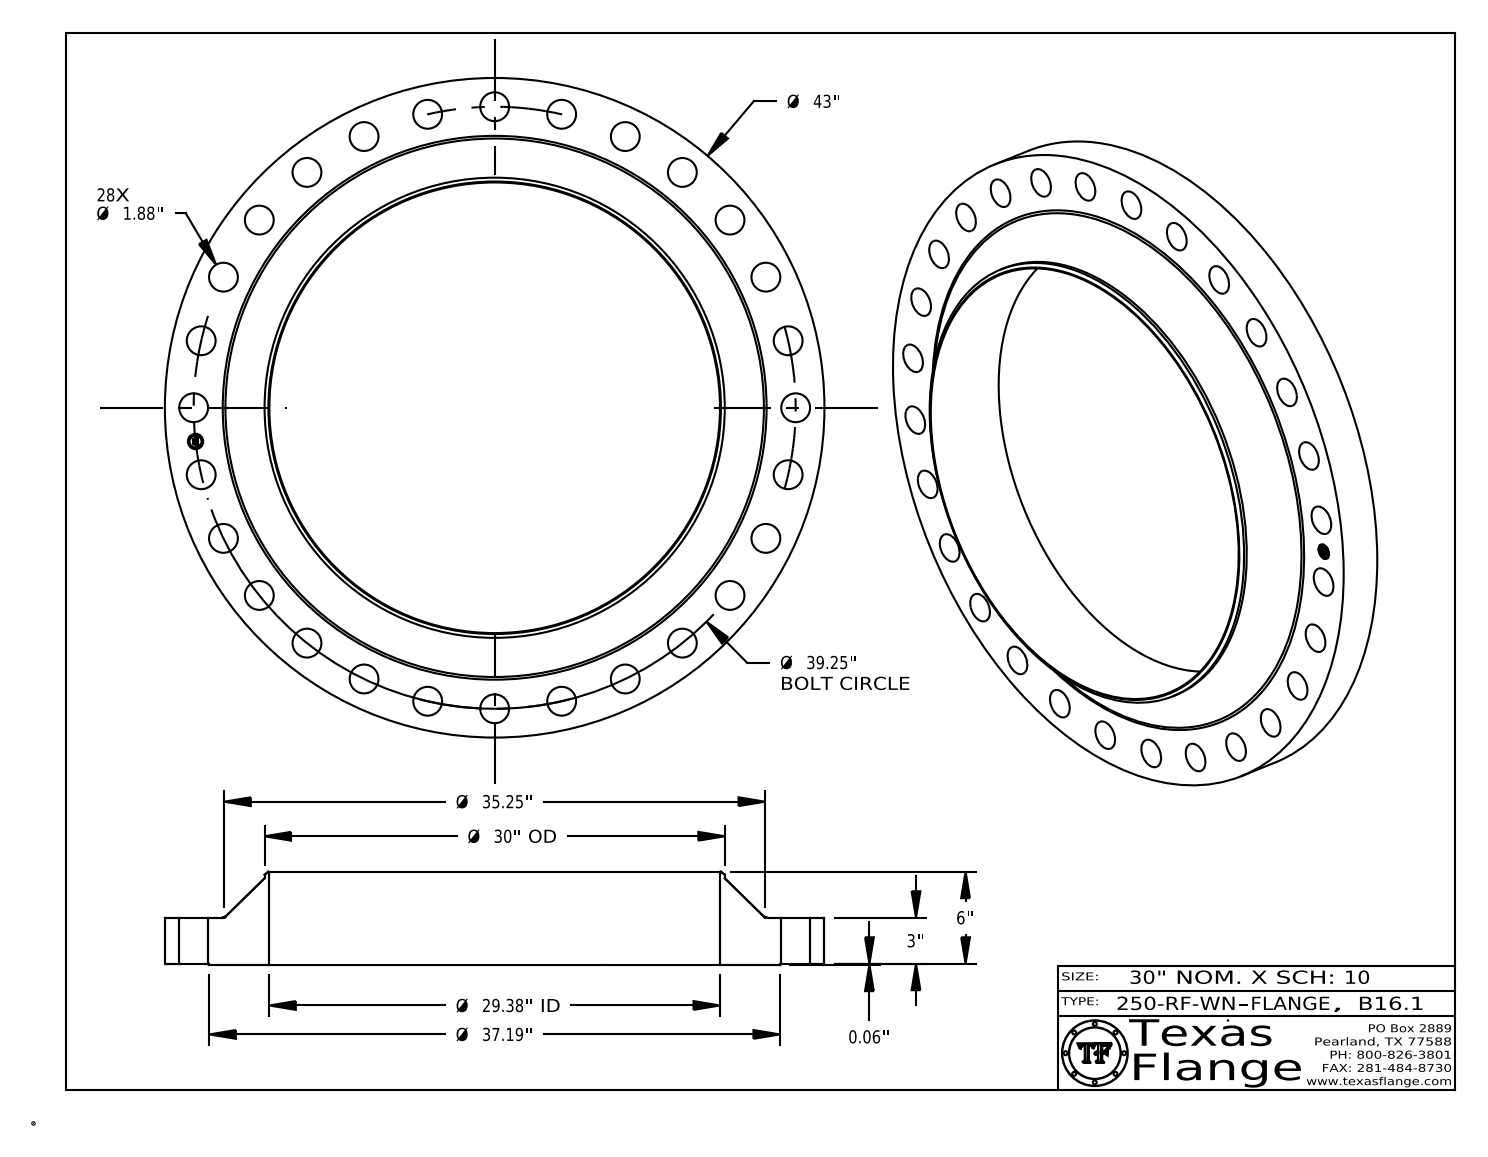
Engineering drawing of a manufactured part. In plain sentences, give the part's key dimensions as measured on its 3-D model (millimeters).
The part is named "250-RF-WN, B16.1". Its 3-D file was written by "CATIA V5 STEP AP203 (CONFIG_CONTROL_DESIGN)". It is 1 solid with 459 faces: 369 planar, 84 cylindrical and 6 other. Overall it measures 1092.2 by 1092.2 by 153.99 millimeters. Its volume is 41 580 000 cubic millimeters and its surface area 1 933 000 square millimeters. Round holes: 28 of diameter 47.75, 1 of diameter 25.4, 1 of diameter 746.15. Round bosses or shafts: 8 of diameter 1.54, 1 of diameter 1092.2, 1 of diameter 944.63, 1 of diameter 762, 1 of diameter 20.01. The main face-to-face distances are 77.79, 76.2, 1.59, 153.99, 152.4, 77.41, 75.82, 0.38, 76.58, 7.58. The hole center spacings are 111.62, 221.84, 329.27, 432.56, 530.41, 898.22, 621.59, 844.14.
